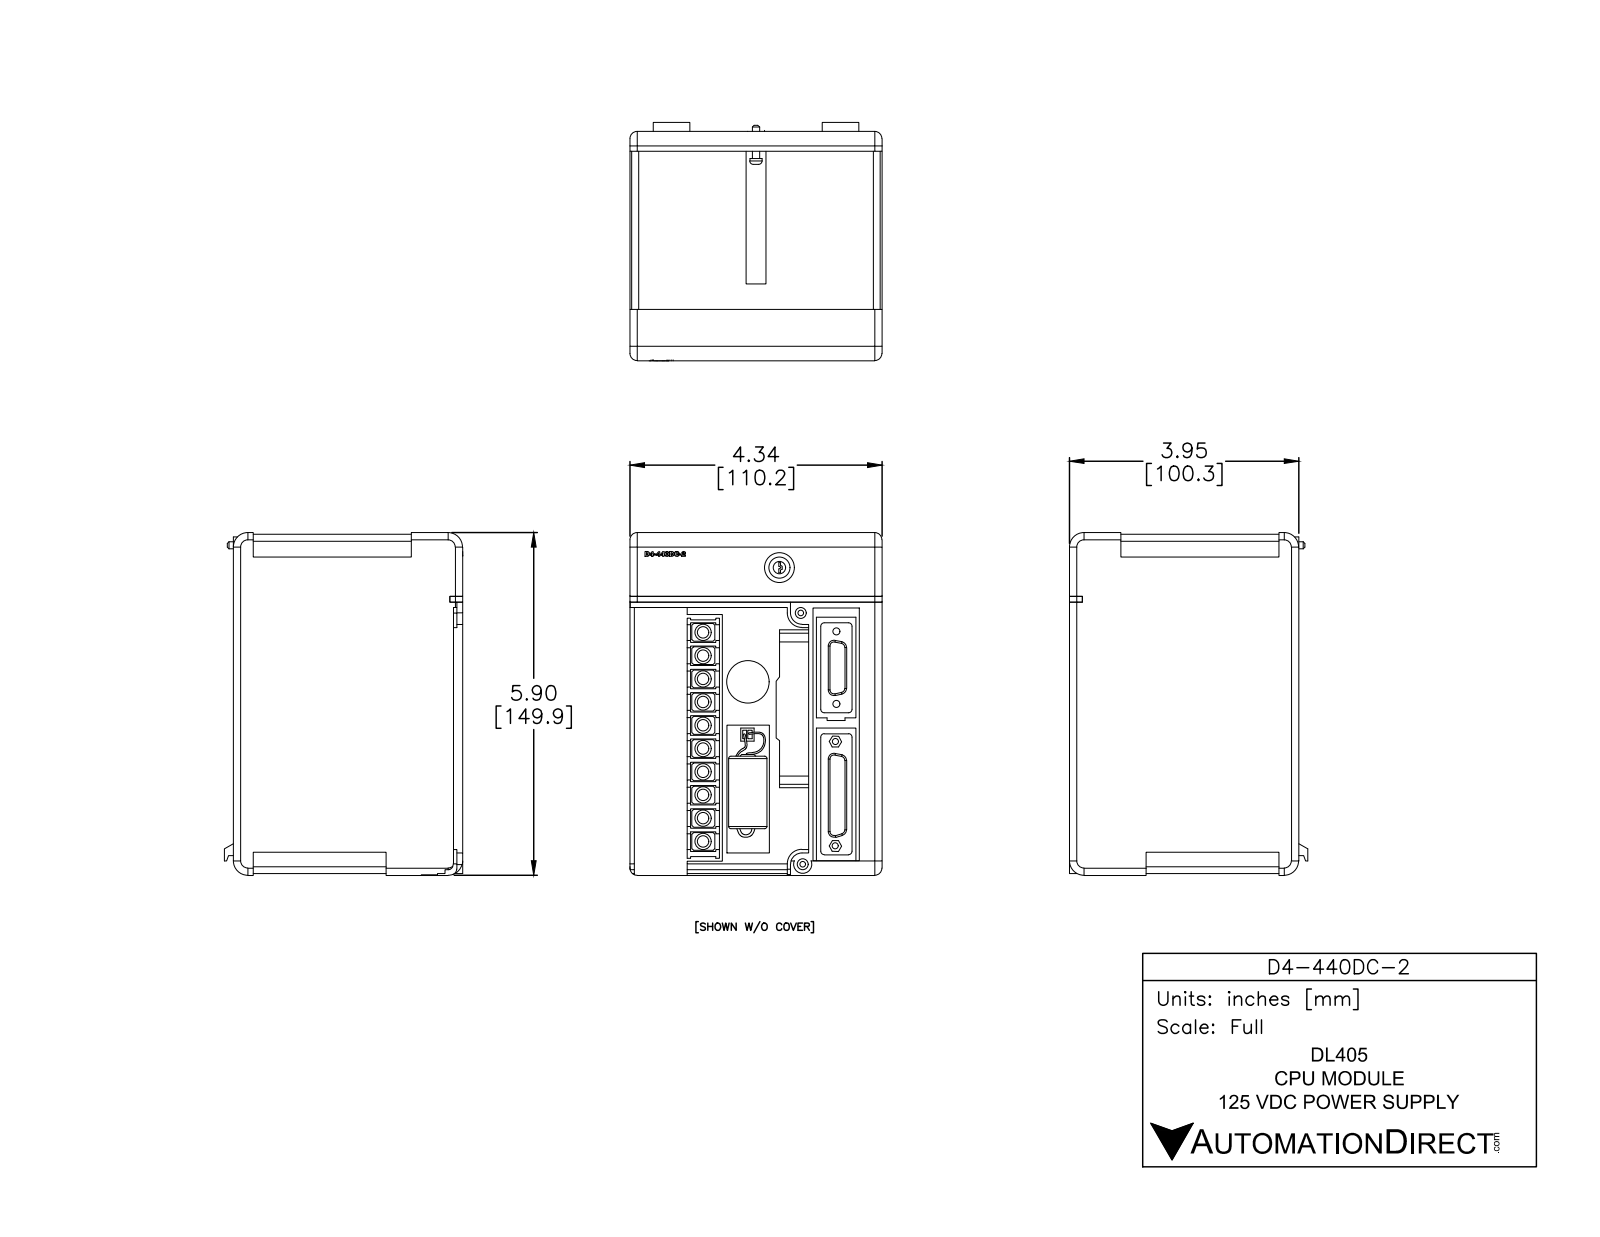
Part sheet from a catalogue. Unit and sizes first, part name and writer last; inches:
Units: inches
Overall size (bounding box): 5.905 × 4.34 × 4.106
Round holes (diameter × count): ⌀0.1 ×2, ⌀0.12 ×2, ⌀0.104 ×1, ⌀0.105 ×1, ⌀0.188 ×1, ⌀0.188 ×1, ⌀0.216 ×1, ⌀0.51 ×1, ⌀0.73 ×1
Round bosses / shafts (diameter × count): ⌀0.279 ×10, ⌀0.66 ×1, ⌀0.365 ×1, ⌀0.212 ×1, ⌀0.123 ×1
Partial cylindrical surfaces — rounded edges, fillets, slot ends (radius × count): R0.1 ×9, R0.06 ×8, R0.125 ×8, R0.03 ×6, R0.25 ×6, R0.12 ×4, R0.2 ×2, R0.145 ×1
Main face-to-face distances: 4.34, 0.03, 5.845, 5.875, 3.95, 0.715, 3.235, 0.45, 3.79, 0.555
Hole centre spacings: 0.644, 0.649, 0.69, 0.861, 1.248, 1.47, 1.497, 1.569
Volume: 90.72 in³ · Surface area: 177.8 in²
Bodies: 3 solids, 782 faces (586 planar, 111 cylindrical, 85 other)
Part name (STEP PRODUCT): D4-440DC-2
STEP written by: SolidWorks 2014 (AUTOMOTIVE_DESIGN)
